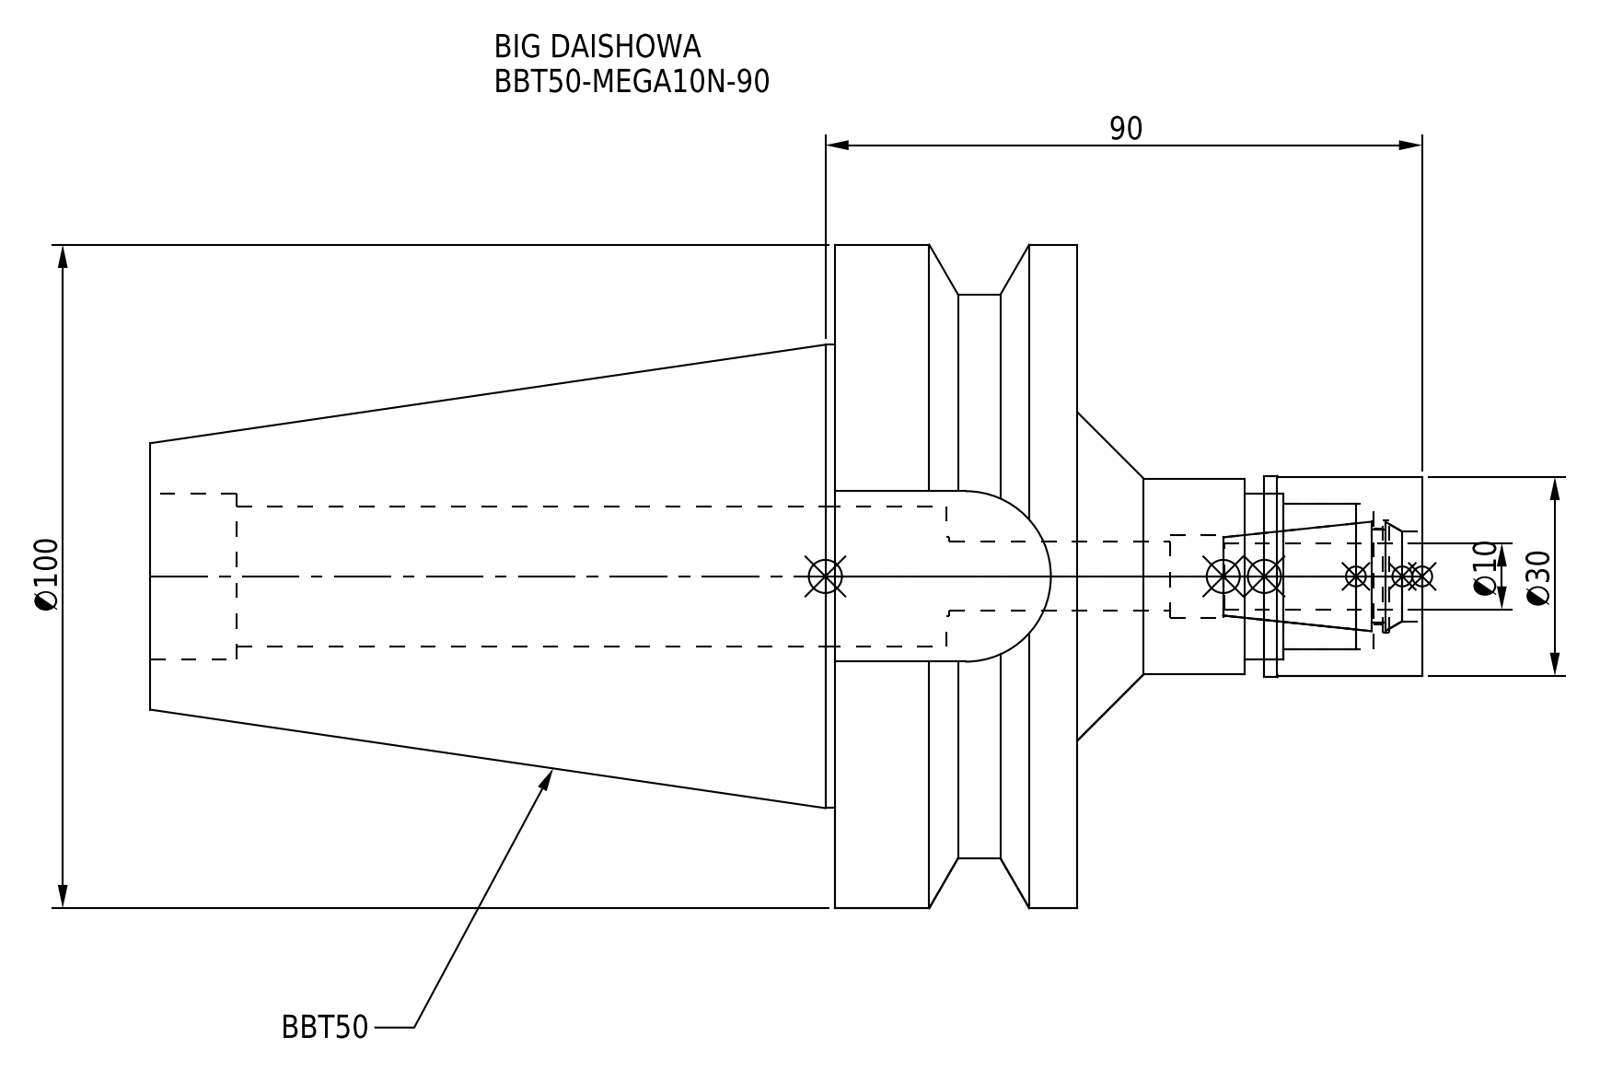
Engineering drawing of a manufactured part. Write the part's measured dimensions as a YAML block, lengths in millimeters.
part_name: "BBT50-MEGA10N-90-100.stp; BBT50MN10090-100_ASM.stp; DXF_TEMP_ASSY_ASM_4_ASM.stp; MGN10_1.stp (+3 more)"
step_written_by: "SolidWorks 2019 (CONFIG_CONTROL_DESIGN)"
units: millimeters
bodies: {solids: 2, faces: 79, planar: 23, cylindrical: 42, other: 14}
overall_size: [191.8, 100, 100]
volume: 486901
surface_area: 63683
round_holes:
  - {diameter: 10.4, count: 1}
  - {diameter: 12, count: 1}
  - {diameter: 12.5, count: 1}
  - {diameter: 13.5, count: 1}
  - {diameter: 14.5, count: 1}
  - {diameter: 17, count: 1}
  - {diameter: 21.2, count: 1}
  - {diameter: 22, count: 1}
  - {diameter: 25, count: 1}
round_bosses_or_shafts:
  - {diameter: 100, count: 1}
  - {diameter: 85, count: 1}
  - {diameter: 69.85, count: 1}
  - {diameter: 30.3, count: 1}
  - {diameter: 30, count: 1}
  - {diameter: 29.5, count: 1}
partial_cylinders:
  - {radius: 12.85, count: 1}
face_to_face_distances: [36.5, 139.8, 103.3, 70.8, 52, 88.5, 191.8, 25.7, 71.8, 19.8]
